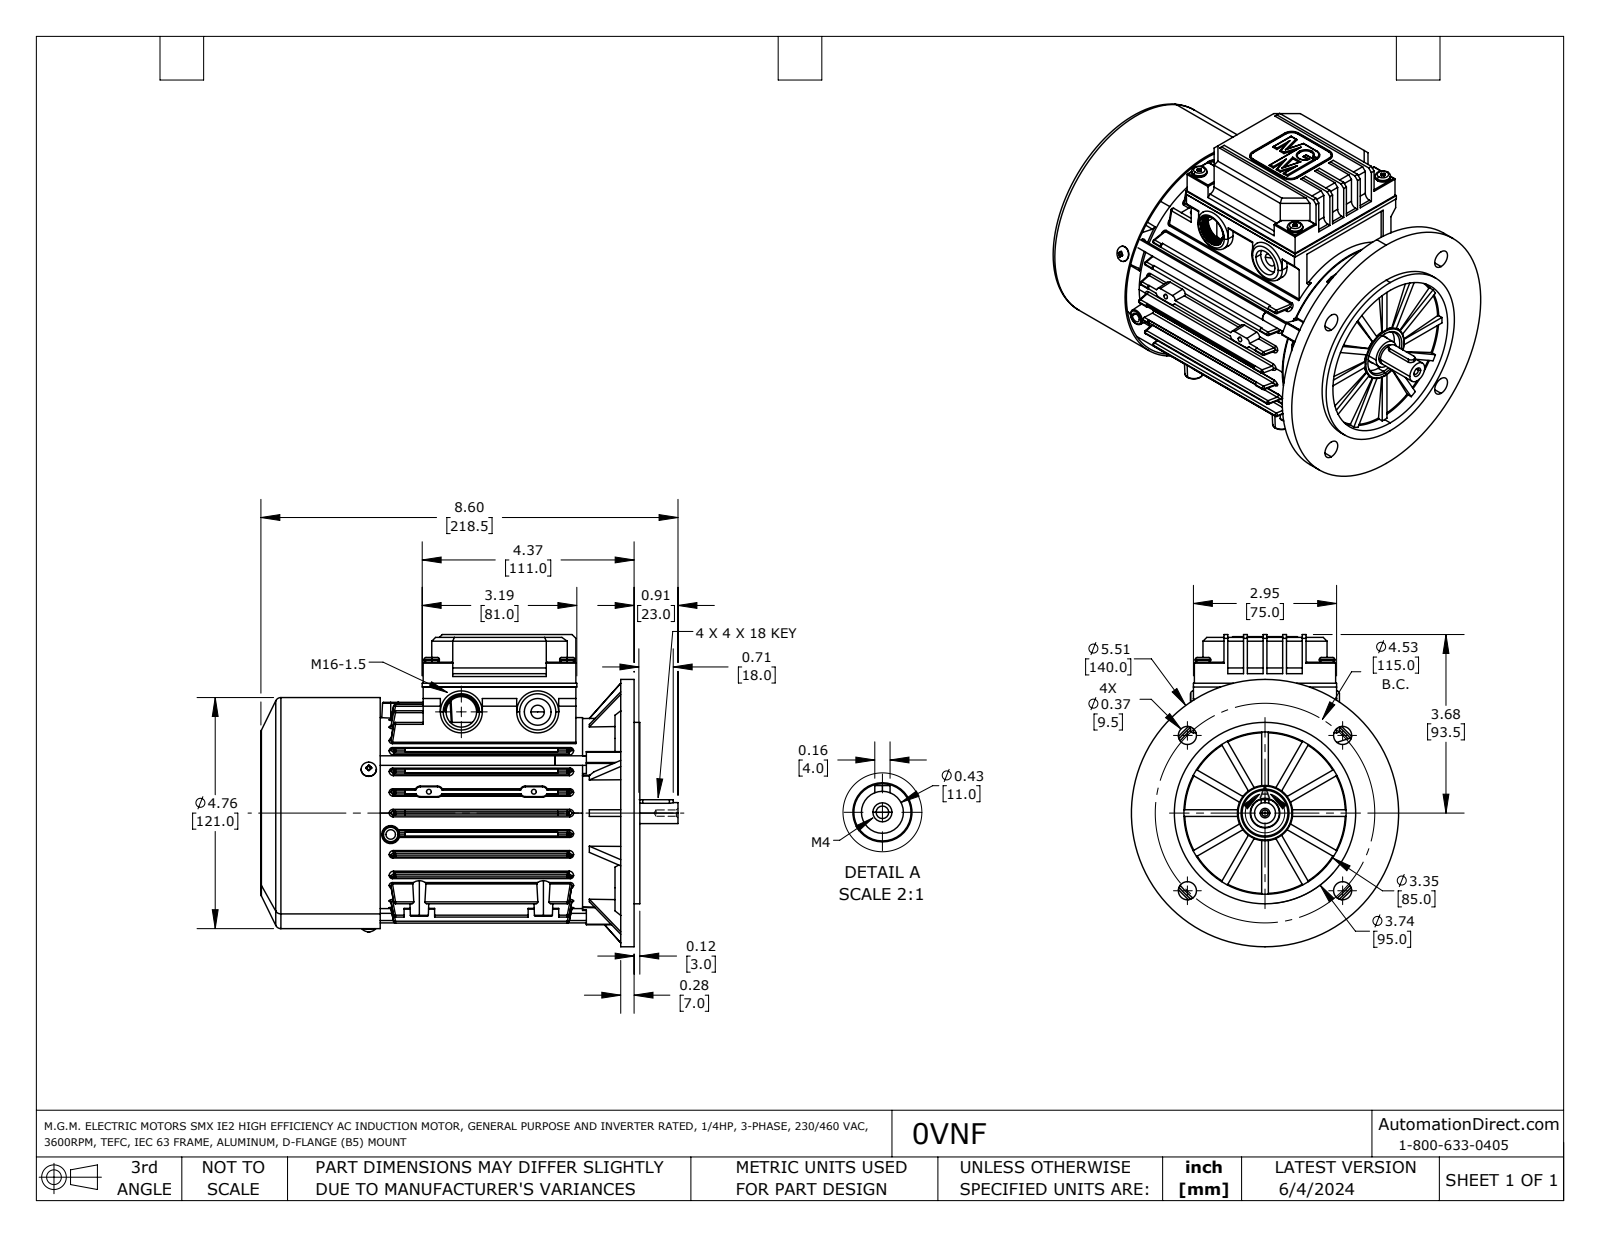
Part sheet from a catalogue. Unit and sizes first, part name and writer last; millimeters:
Units: millimetres
Overall size (bounding box): 218.5 × 163.5 × 140
Round holes (diameter × count): ⌀3 ×12, ⌀3.3 ×8, ⌀4 ×7, ⌀5.5 ×7, ⌀5 ×6, ⌀9.5 ×4, ⌀3.2 ×3, ⌀4.2 ×3, ⌀6 ×3, ⌀7 ×3, ⌀2.5 ×2, ⌀16 ×2
Round bosses / shafts (diameter × count): ⌀3 ×10, ⌀8 ×7, ⌀3.5 ×4, ⌀5 ×3, ⌀2 ×3, ⌀140 ×1, ⌀121 ×1, ⌀100 ×1
Partial cylindrical surfaces — rounded edges, fillets, slot ends (radius × count): R1 ×281, R0.4 ×42, R0.5 ×36, R0.2 ×32, R0.1 ×16, R0.8 ×16, R0.4 ×12, R0.9 ×12
Main face-to-face distances: 2, 11, 22, 24, 33, 13, 20, 3.5, 1.5, 100
Hole centre spacings: 94.4, 11.5, 11.6, 13.7, 19.5, 28.5, 30.8, 31
Volume: 521 300 mm³ · Surface area: 330 300 mm²
Bodies: 22 solids, 3150 faces (1116 planar, 1031 cylindrical, 1003 other)
Part name (STEP PRODUCT): 0VNF
STEP written by: SolidWorks 2021 (AUTOMOTIVE_DESIGN)
